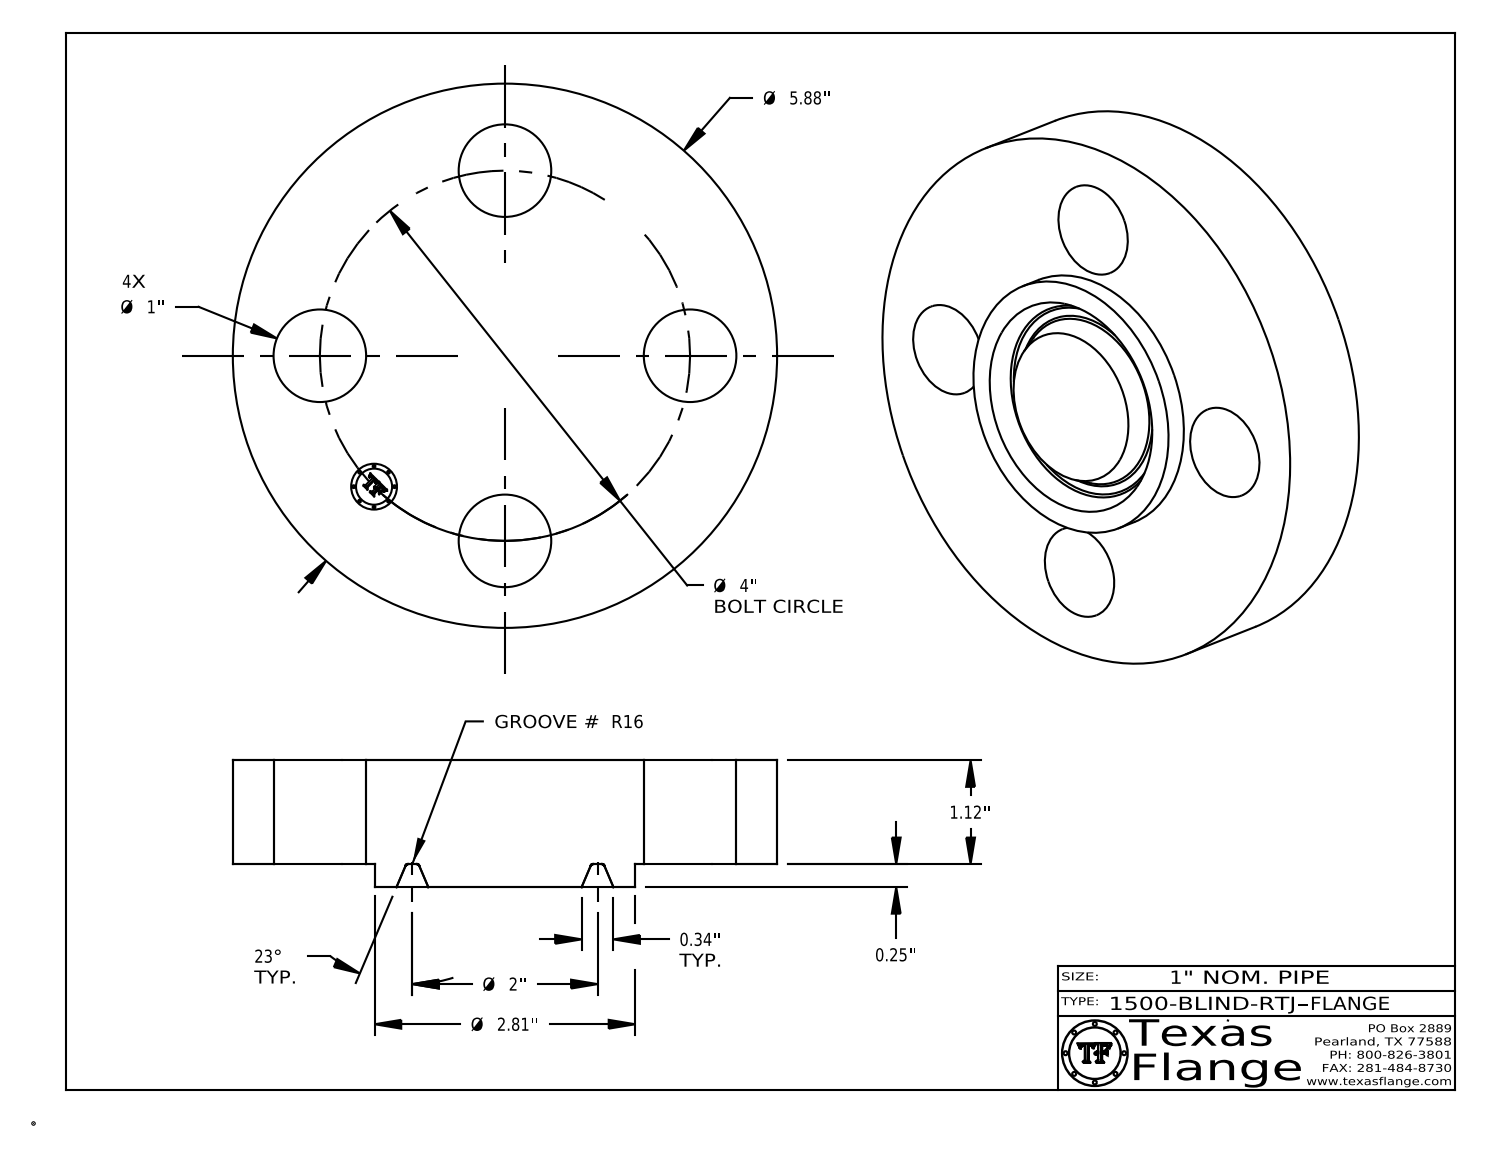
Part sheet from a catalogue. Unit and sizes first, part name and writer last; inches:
Units: inches
Overall size (bounding box): 5.88 × 5.88 × 1.37
Round holes (diameter × count): ⌀1 ×4, ⌀0.495 ×1
Round bosses / shafts (diameter × count): ⌀0.03 ×8, ⌀5.88 ×1, ⌀2.813 ×1, ⌀0.39 ×1
Main face-to-face distances: 1.12, 0.25, 1.37, 0.015, 1.355, 1.105, 0.148, 0.145, 0.027, 0.096
Hole centre spacings: 2.828, 1.531, 3.695, 4
Volume: 28.07 in³ · Surface area: 87.11 in²
Bodies: 1 solid, 410 faces (370 planar, 32 cylindrical, 8 other)
Part name (STEP PRODUCT): 1500-BLIND-RTJ
STEP written by: CATIA V5 STEP AP214 (AUTOMOTIVE_DESIGN)
